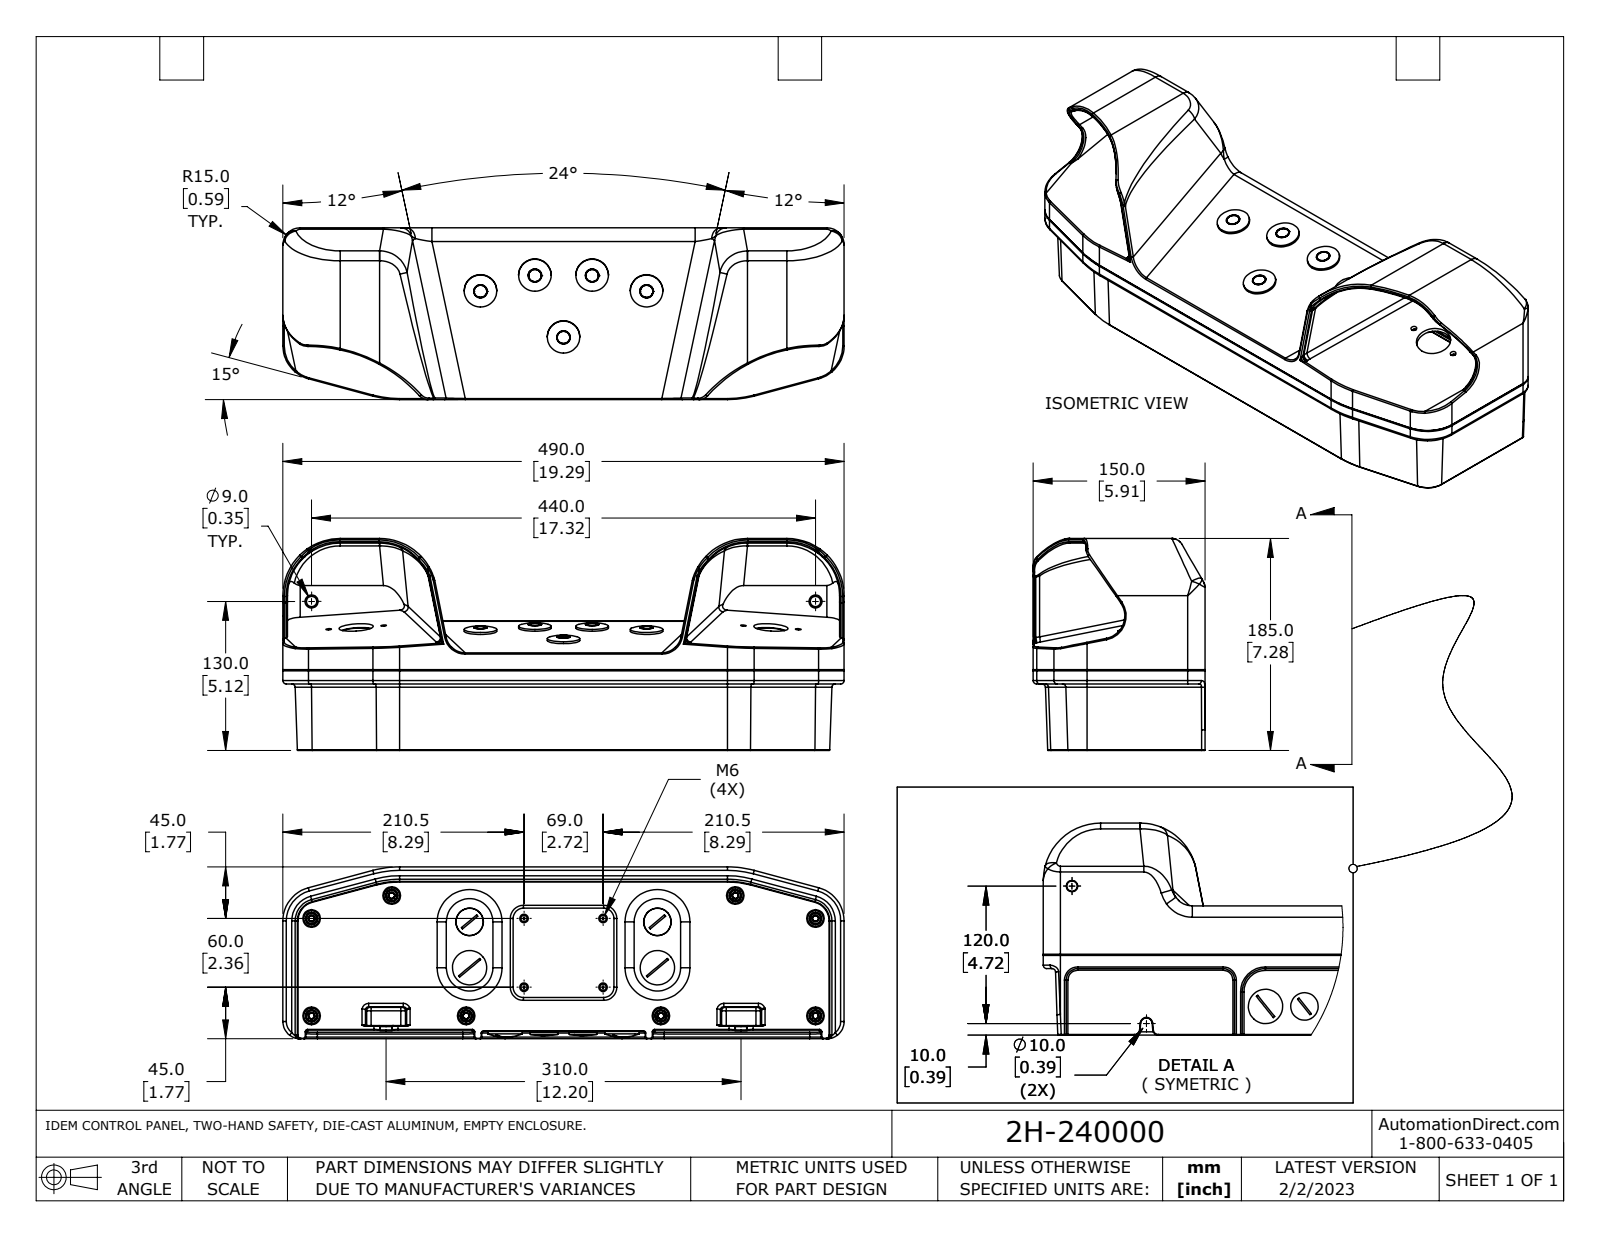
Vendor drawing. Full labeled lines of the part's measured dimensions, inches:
Part name (STEP PRODUCT): 2H-240000
STEP written by: SolidWorks 2021 (AUTOMOTIVE_DESIGN)
Units: inches
Bodies: 1 solid, 1052 faces (336 planar, 358 cylindrical, 358 other)
Overall size (bounding box): 19.291 × 7.283 × 5.906
Volume: 414.8 in³ · Surface area: 641.3 in²
Round holes (diameter × count): ⌀0.528 ×8, ⌀0.433 ×5, ⌀0.626 ×5, ⌀0.886 ×5, ⌀0.197 ×4, ⌀0.217 ×4, ⌀0.571 ×4, ⌀0.354 ×2, ⌀0.701 ×2, ⌀0.78 ×2, ⌀0.969 ×2, ⌀1.181 ×2
Round bosses / shafts (diameter × count): ⌀0.394 ×8, ⌀1.118 ×5, ⌀0.878 ×5, ⌀0.465 ×5, ⌀1.181 ×4, ⌀0.945 ×4, ⌀0.906 ×4, ⌀0.709 ×4
Partial cylindrical surfaces — rounded edges, fillets, slot ends (radius × count): R0.02 ×81, R0.059 ×35, R0.118 ×22, R0.047 ×15, R0.394 ×10, R0.197 ×9, R0.157 ×8, R0.787 ×7
Main face-to-face distances: 0.157, 0.098, 5.906, 0.256, 7.126, 5.65, 7.028, 7.283, 7.185, 0.315
Hole centre spacings: 1.95, 3.878, 1.969, 2.378, 3.279, 5.709, 17.323, 0.945
